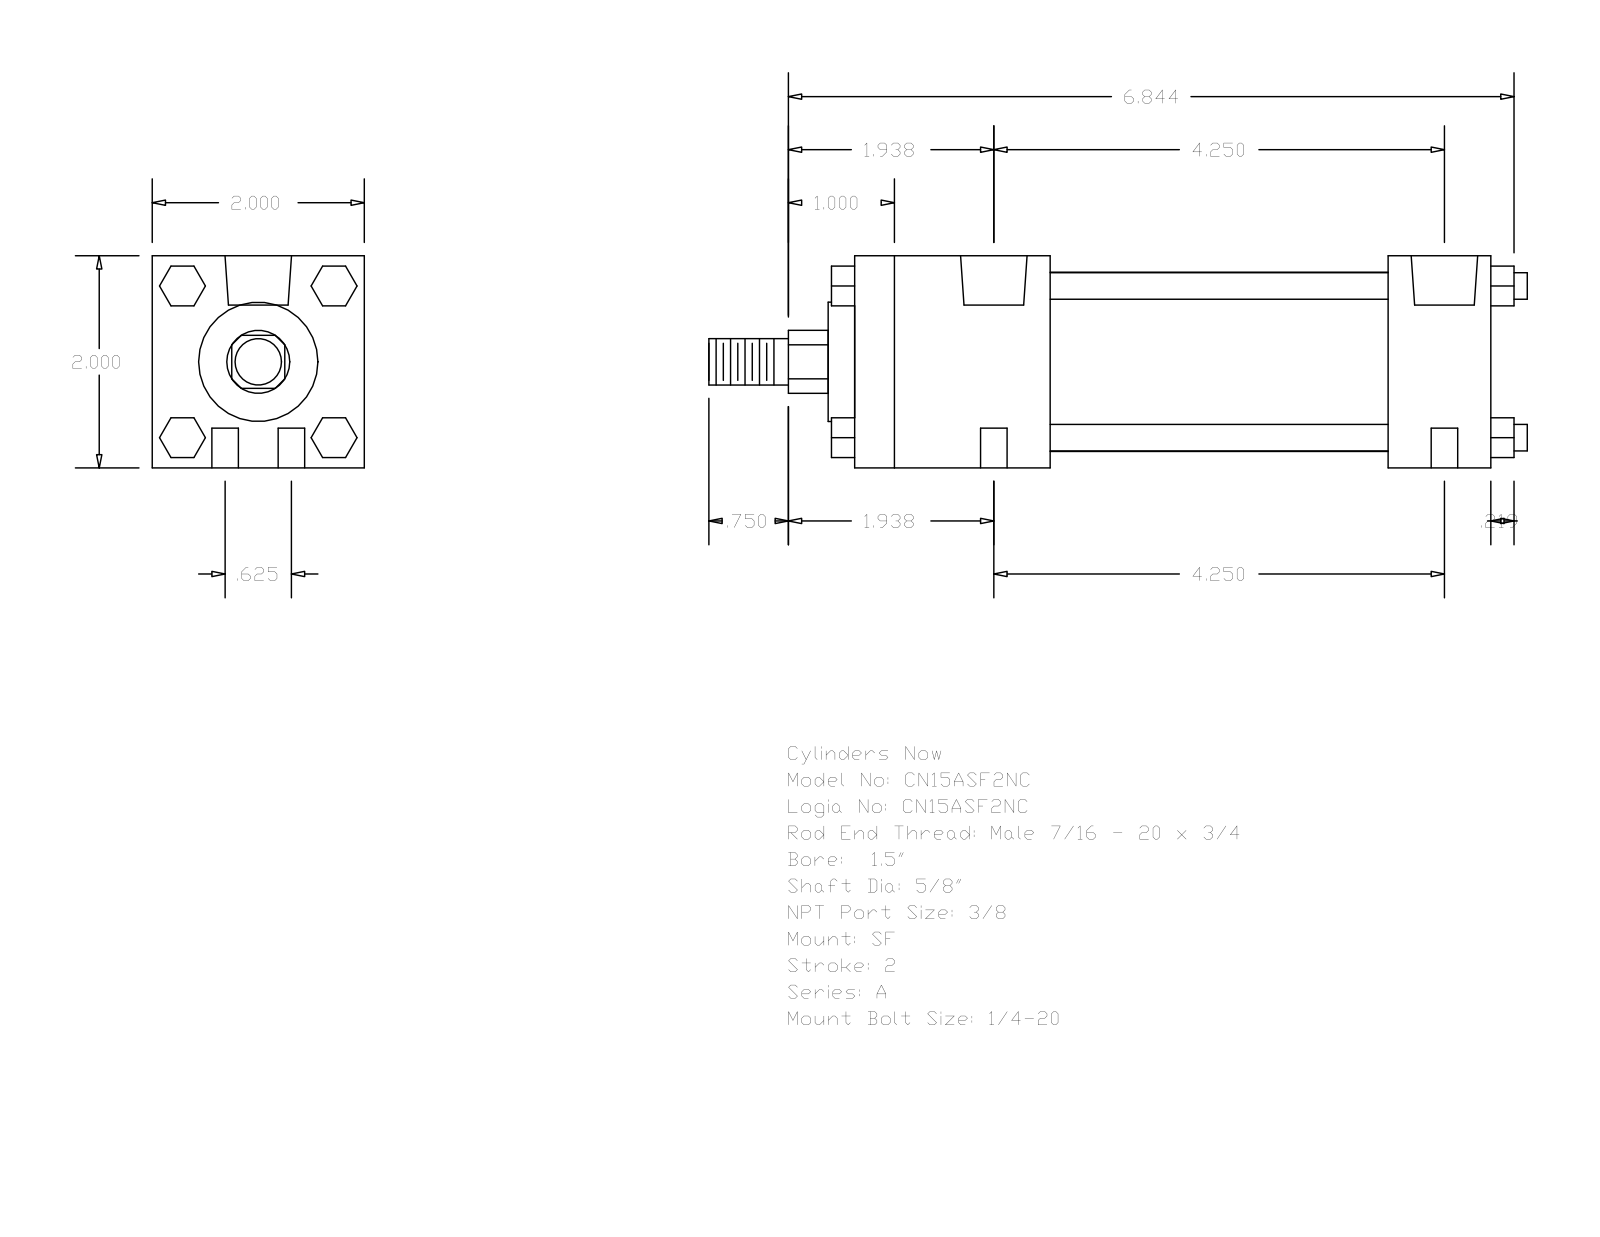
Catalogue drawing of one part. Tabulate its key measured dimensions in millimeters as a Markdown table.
| quantity | value |
| --- | --- |
| part name | A_SF__0150_0.625 |
| STEP written by | GSSL Pune (CONFIG_CONTROL_DESIGN) |
| units | millimeters |
| bodies | 0 solids, 124 faces (94 planar, 30 cylindrical, 0 other) |
| overall size | 196.06 × 50.8 × 50.8 |
| round holes (diameter × count) | 6.35 × 4, 5.56 × 2, 15.93 × 2 |
| round bosses / shafts (diameter × count) | 6.35 × 4, 42.93 × 1, 28.57 × 1, 15.88 × 1, 11.11 × 1 |
| partial cylindrical surfaces (radius × count) | 7.54 × 1 |
| main face-to-face distances | 50.8, 152.4, 46.83, 127.79, 80.96, 105.57, 24.61, 6.35, 9.52, 53.18 |
| hole center spacings | 7.94, 108.24, 107.95, 15.88, 109.11, 100.01 |
